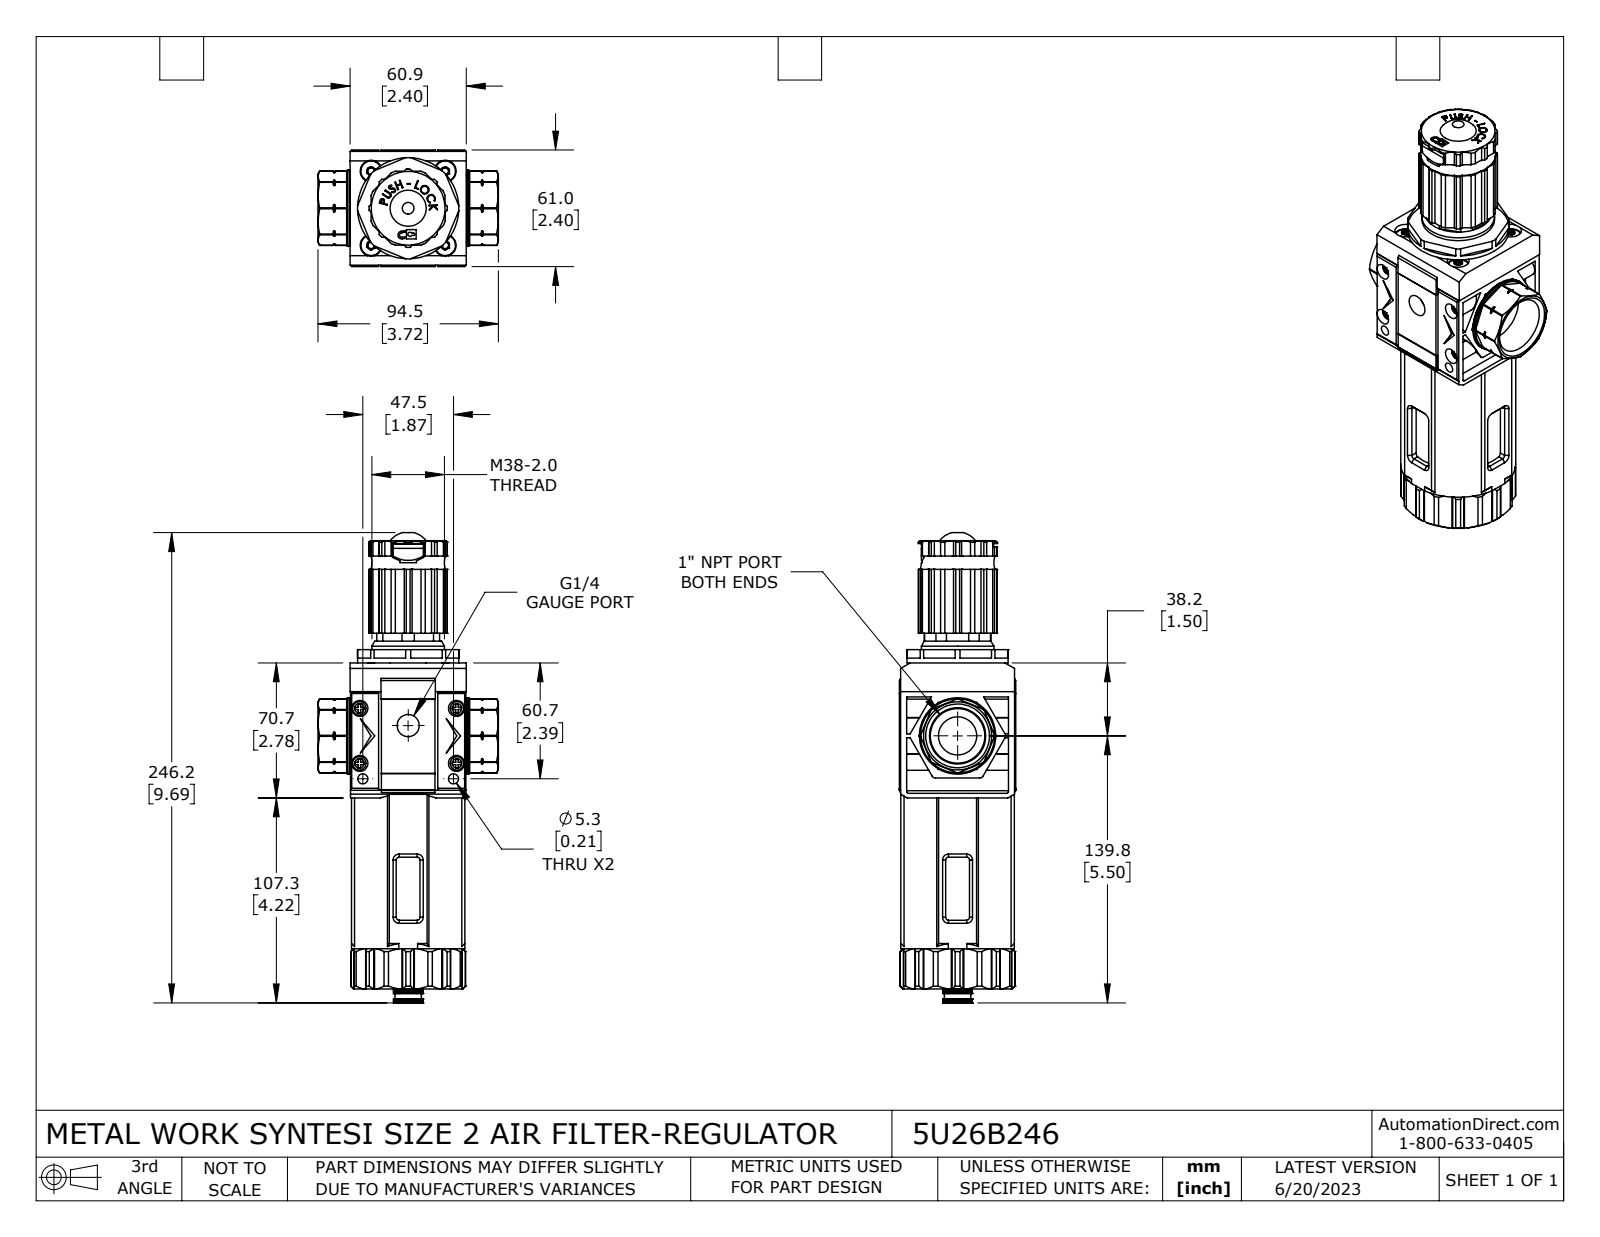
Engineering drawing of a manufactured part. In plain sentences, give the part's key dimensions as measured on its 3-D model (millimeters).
The part is named "5U26B246". Its 3-D file was written by "SolidWorks 2021 (CONFIG_CONTROL_DESIGN)". It is 15 solids with 2089 faces: 1272 planar, 521 cylindrical and 296 other. Overall it measures 246.2 by 94.5 by 61 millimeters. Its volume is 472 100 cubic millimeters and its surface area 145 000 square millimeters. Round holes: 4 of diameter 3.3, 4 of diameter 4.2, 4 of diameter 8.4, 4 of diameter 11.4, 2 of diameter 5.3, 1 of diameter 3.2, 1 of diameter 7, 1 of diameter 8.7, 1 of diameter 11.6, 1 of diameter 20, 1 of diameter 31.8, 1 of diameter 35.8. Round bosses or shafts: 4 of diameter 7, 4 of diameter 4.8, 4 of diameter 3.8, 1 of diameter 53, 1 of diameter 40, 1 of diameter 38, 1 of diameter 35, 1 of diameter 31.7. Partial cylindrical surfaces (rounded edges, fillets, slot ends): 28 of radius 0.3, 16 of radius 0.5, 8 of radius 1.5, 4 of radius 1.8, 4 of radius 4.9, 4 of radius 20.5, 2 of radius 0.2, 2 of radius 2. The main face-to-face distances are 134.7, 60.7, 79, 81.4, 53.3, 28.7, 55.7, 61, 0.8, 149.7. The hole center spacings are 27.4, 38.8, 8.3, 26.8, 28.8, 32.1, 36.7, 36.9.
